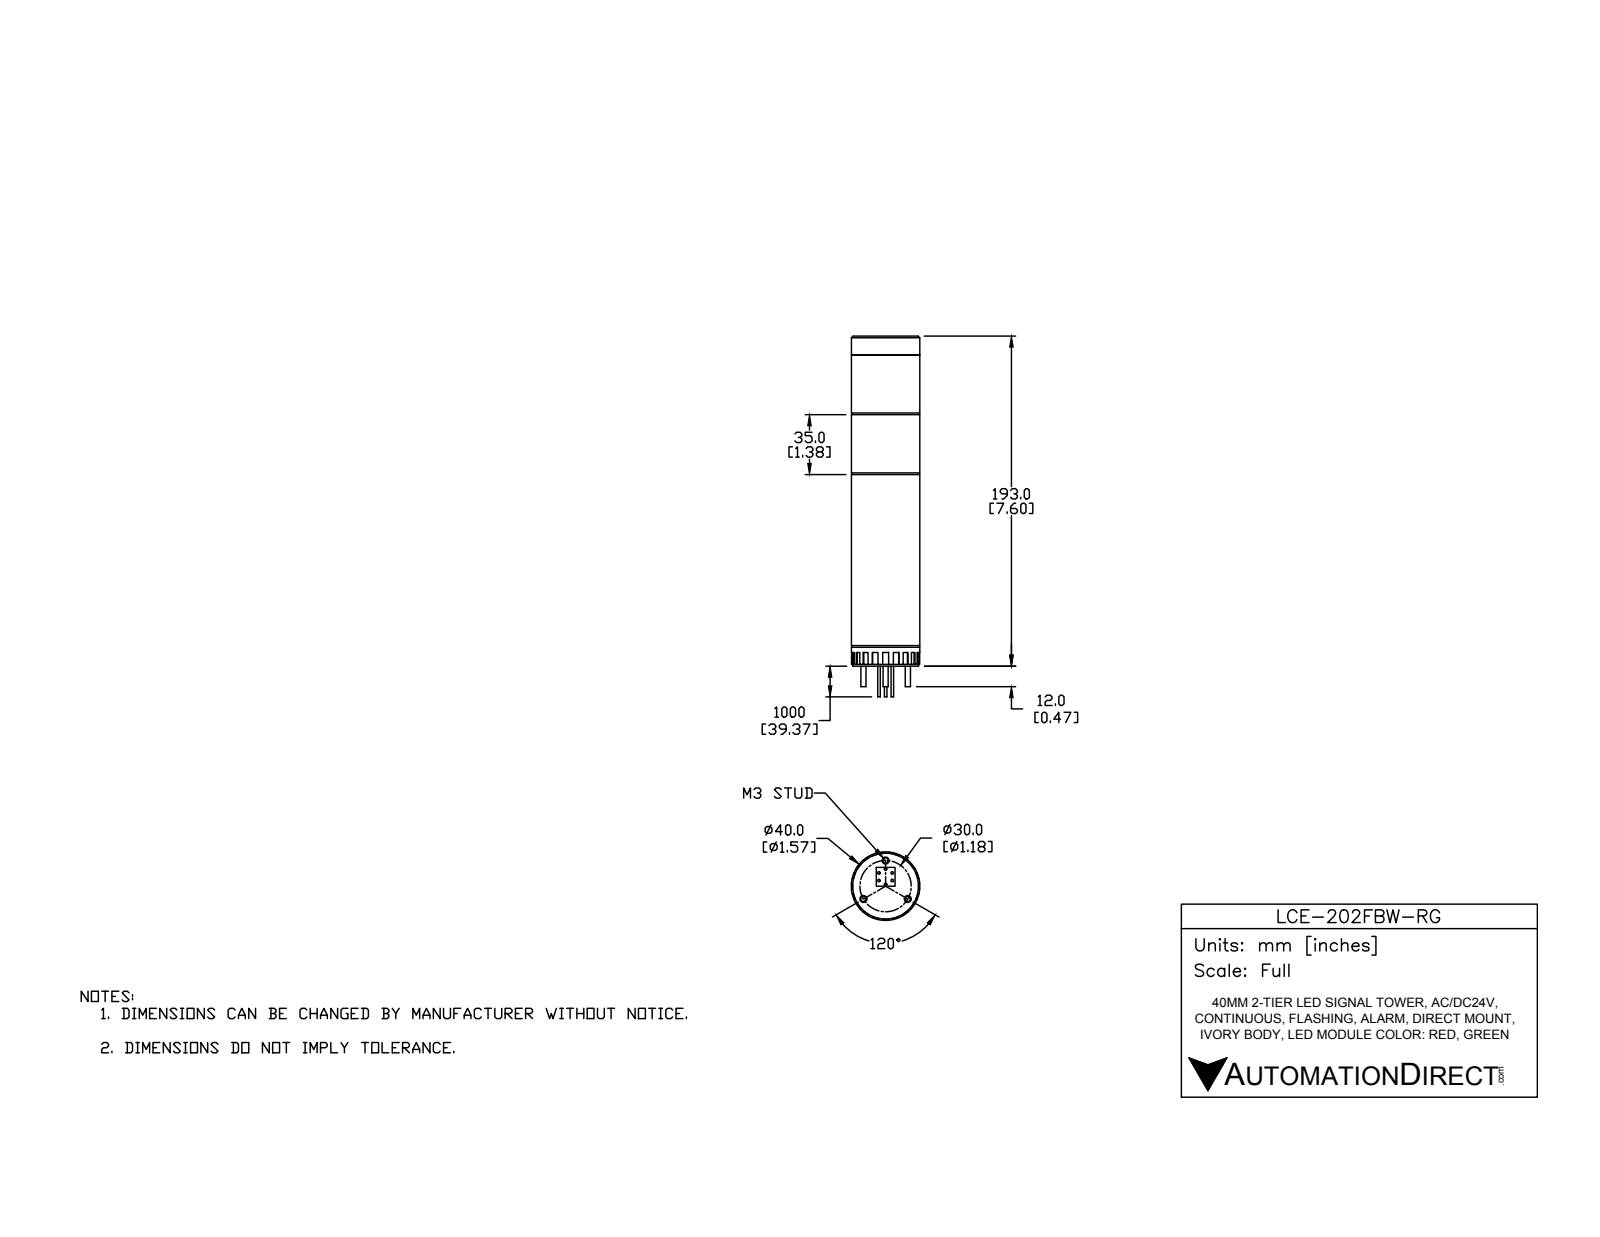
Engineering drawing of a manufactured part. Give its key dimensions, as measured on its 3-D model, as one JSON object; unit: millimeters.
{"part_name": "LCE-202FBW-RG", "step_written_by": "SolidWorks 2016 (AUTOMOTIVE_DESIGN)", "units": "millimeters", "bodies": {"solids": 23, "faces": 210, "planar": 152, "cylindrical": 54, "other": 4}, "overall_size": [211, 40, 40], "volume_mm3": 241150, "surface_area_mm2": 48365, "round_holes": [[4, 3], [8, 1]], "round_bosses_or_shafts": [[1.5, 10], [3, 3], [40, 1], [39.5, 1], [38.5, 1], [5.5, 1]], "face_to_face_distances": [1, 35, 34, 101, 136, 11, 181, 112, 147, 36], "hole_center_spacings": [15, 25.98]}
